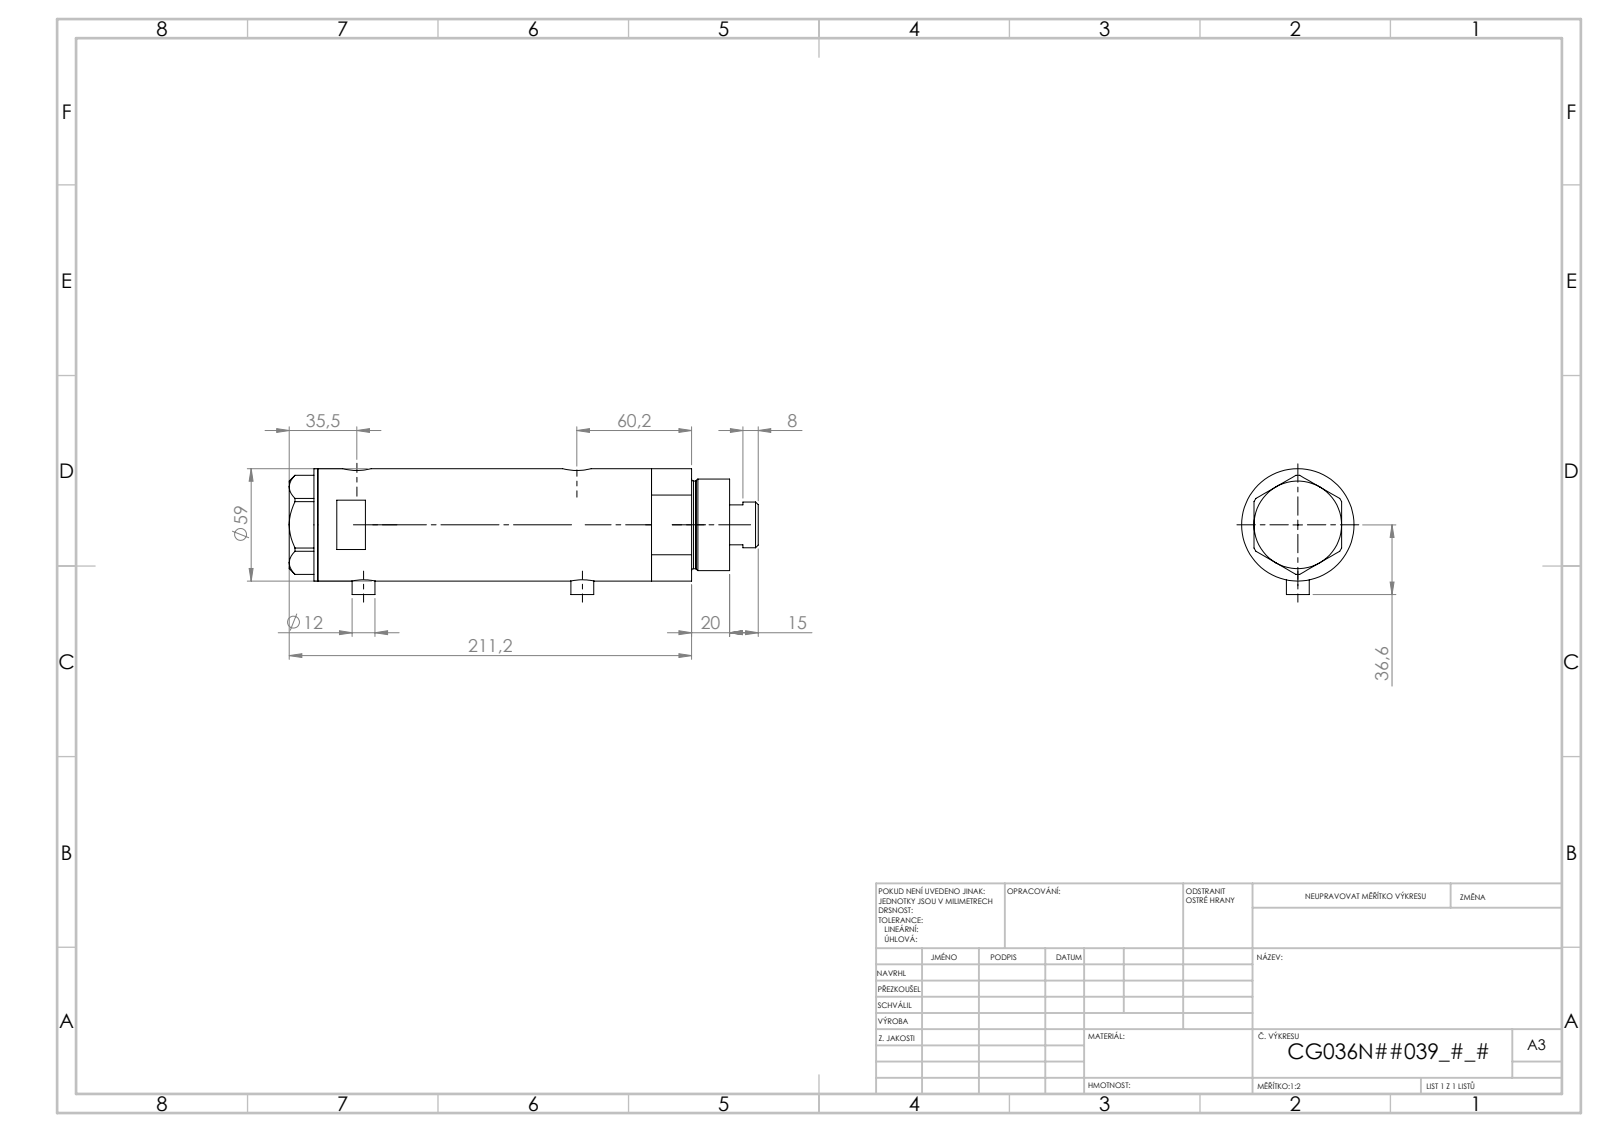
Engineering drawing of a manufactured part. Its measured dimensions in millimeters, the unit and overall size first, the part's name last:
Units: millimetres
Overall size (bounding box): 202.42 × 60.1 × 59
Round holes (diameter × count): ⌀5 ×2, ⌀9.73 ×2, ⌀12.5 ×2, ⌀15 ×2, ⌀8.5 ×1, ⌀25 ×1, ⌀26.5 ×1, ⌀36 ×1, ⌀40 ×1, ⌀52 ×1
Round bosses / shafts (diameter × count): ⌀12 ×2, ⌀59 ×1, ⌀48 ×1, ⌀46 ×1, ⌀24 ×1
Main face-to-face distances: 23.5, 15, 38.5, 111.34, 96.34, 72.84, 187.42, 172.42, 148.92, 76.08
Hole centre spacings: 2.9, 3.5, 71.15, 74.05, 74.65, 77.55, 2.89, 2.91
Volume: 457 213 mm³ · Surface area: 96 596 mm²
Bodies: 4 solids, 126 faces (53 planar, 53 cylindrical, 20 other)
Part name (STEP PRODUCT): V270CG_BACK; V270CG_VC; V270CG_FRONT; V270CG_MIDDLE
STEP written by: SolidWorks 2019 (CONFIG_CONTROL_DESIGN)
